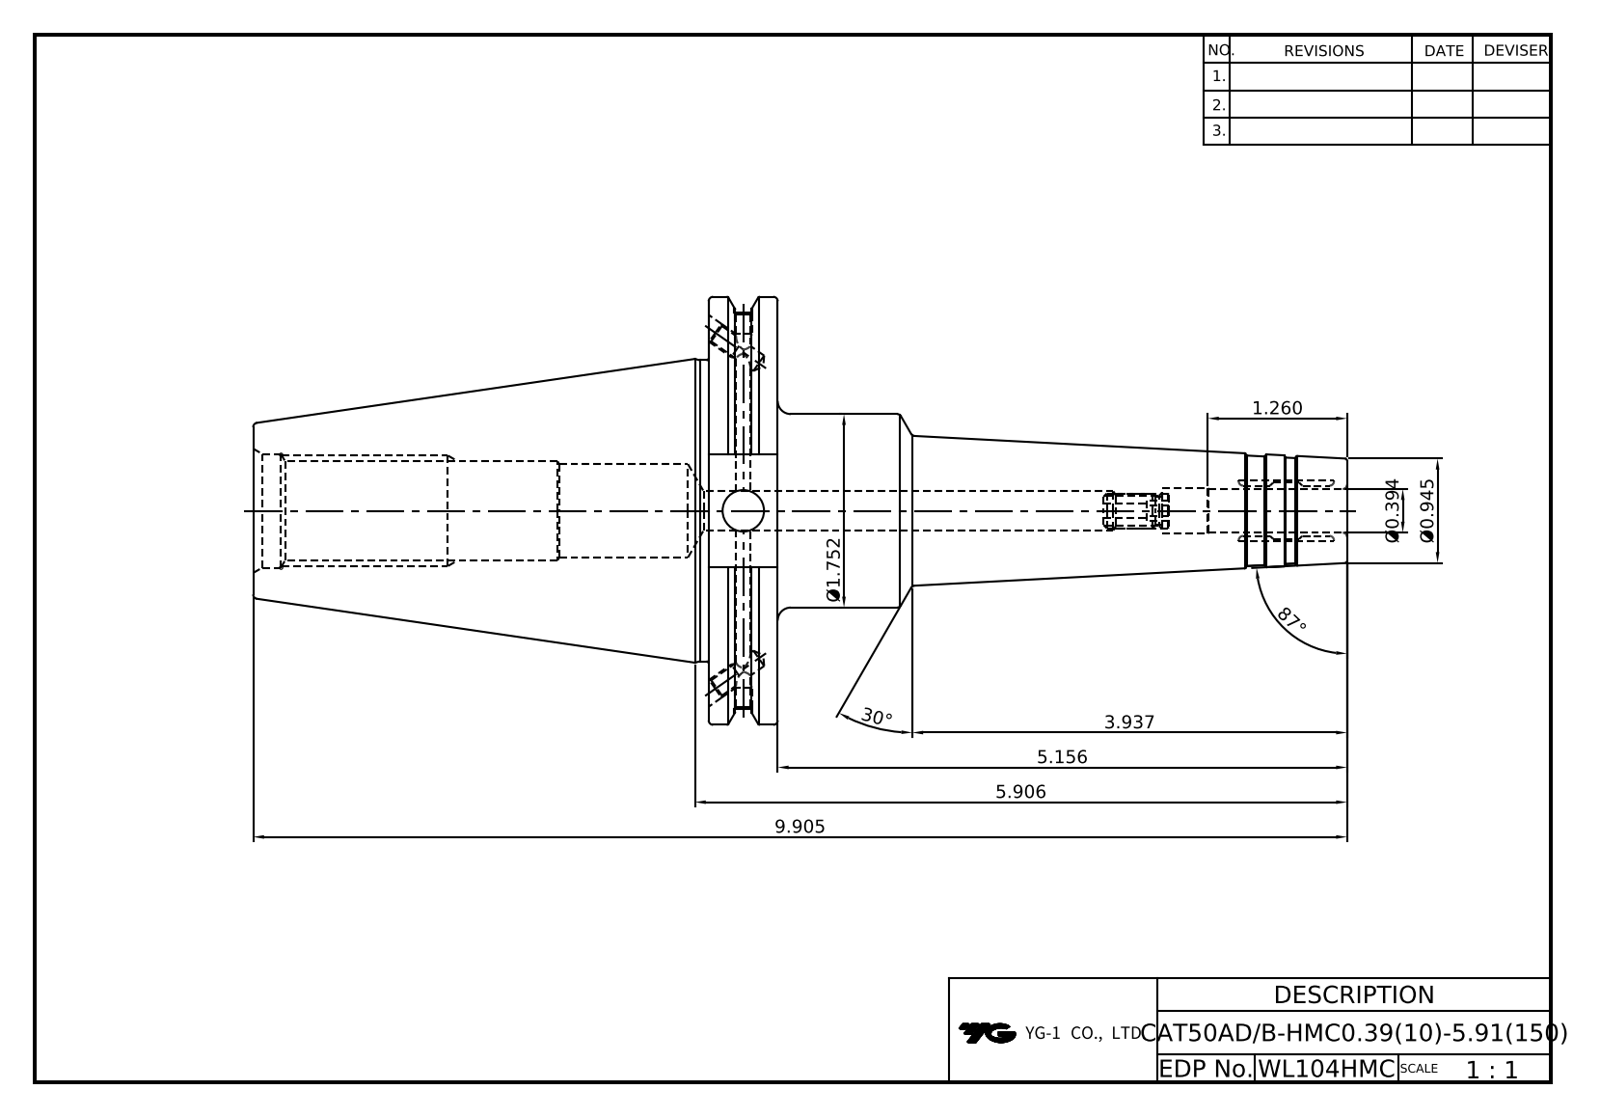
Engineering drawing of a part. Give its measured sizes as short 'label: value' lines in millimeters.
name: LO-CAT50ADB-HMC10-150
written by: Autodesk Inventor 2025 (AUTOMOTIVE_DESIGN)
unit: mm
bodies: 1 solid, 107 faces (37 planar, 28 cylindrical, 42 other)
size: 251.6 × 98.42 × 94.69
volume: 430 636 mm³; area: 60 877 mm²
holes: 2× ⌀3.24, 2× ⌀4.13, 2× ⌀4.2, 2× ⌀5, 1× ⌀6.92, 1× ⌀9, 1× ⌀9.53, 1× ⌀10, 1× ⌀10.6, 1× ⌀21.5, 1× ⌀21.97, 1× ⌀26.2
bosses: 1× ⌀98.42, 1× ⌀91.29, 1× ⌀69.25, 1× ⌀44.5
face distances: 15.88, 104.77, 120.65, 73.03, 251.6, 146.83, 130.95, 25.9, 110.82, 6.05
